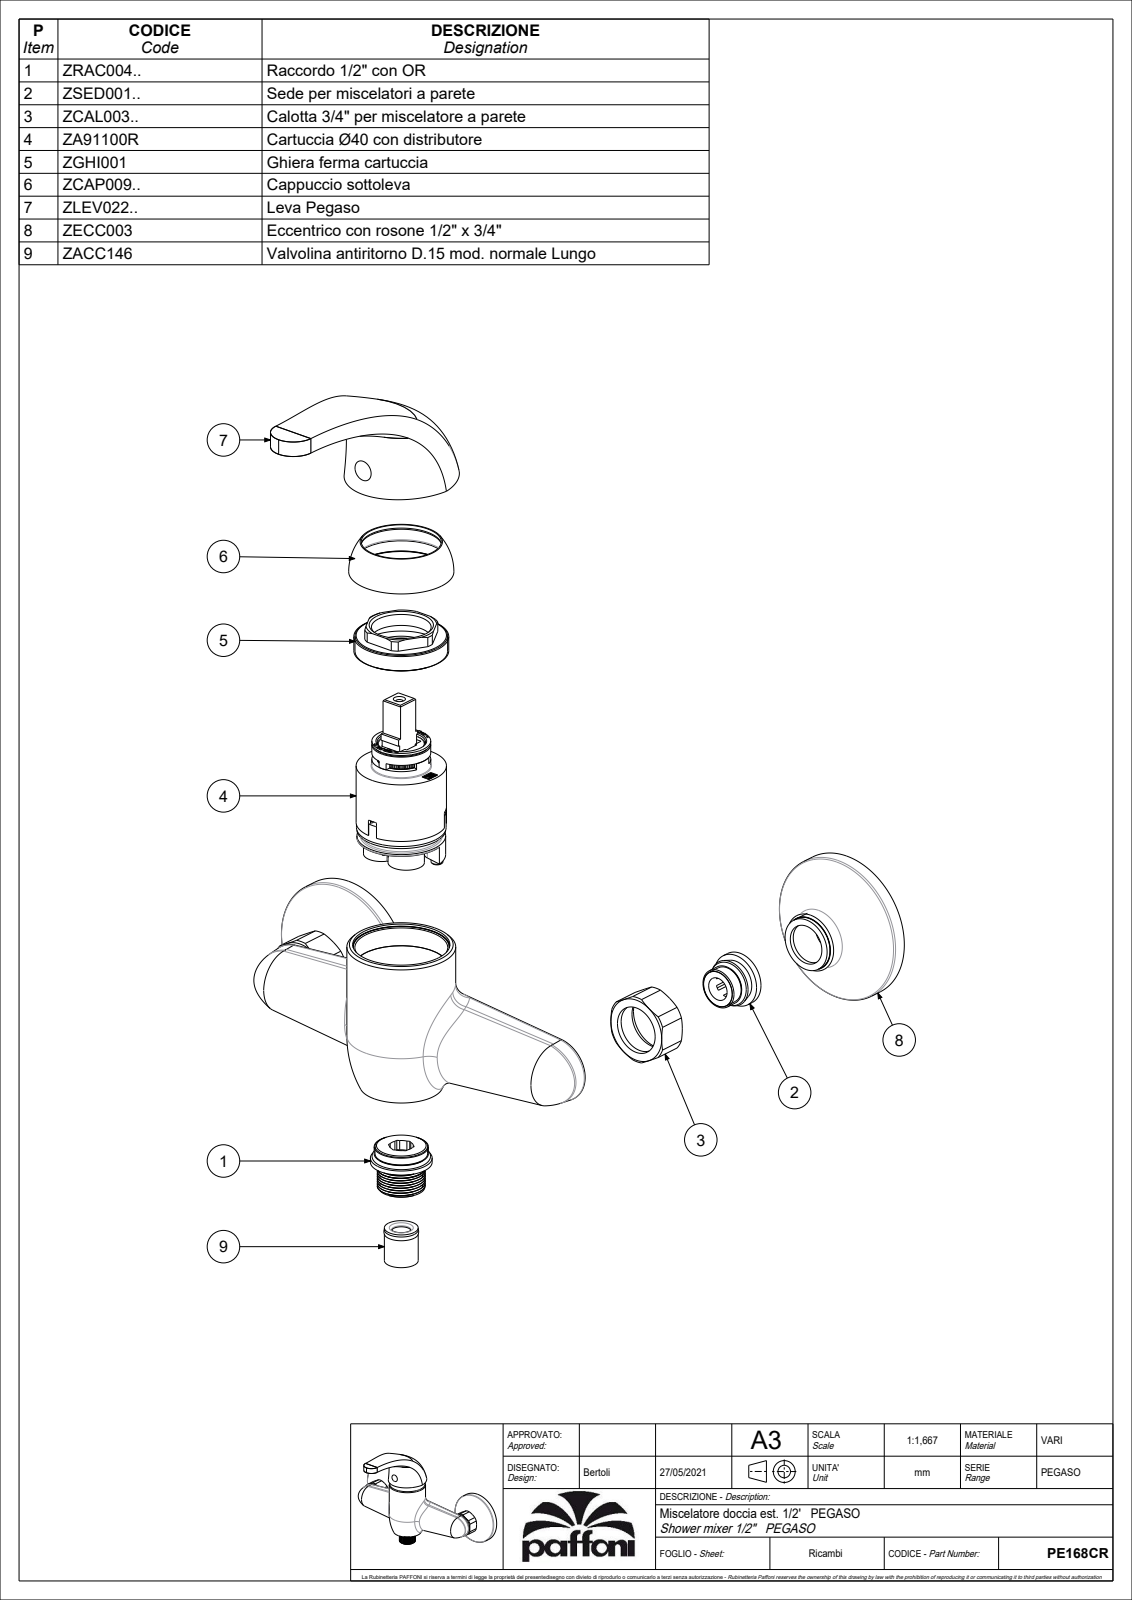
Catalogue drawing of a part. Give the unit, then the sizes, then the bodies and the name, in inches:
Units: inches
Overall size (bounding box): 8.504 × 6.198 × 5.377
Round holes (diameter × count): ⌀1.051 ×2, ⌀0.236 ×1
Round bosses / shafts (diameter × count): ⌀0.827 ×3, ⌀2.598 ×2, ⌀1.039 ×2, ⌀1.874 ×1, ⌀1.063 ×1, ⌀0.315 ×1, ⌀0.197 ×1
Partial cylindrical surfaces — rounded edges, fillets, slot ends (radius × count): R0.039 ×8, R0.61 ×2, R0.154 ×1
Main face-to-face distances: 1.142, 1.358, 1.299, 0.059, 0.914, 2.953, 0.807, 2.106, 2.165, 3.248
Hole centre spacings: 3.831, 5.906
Volume: 23.52 in³ · Surface area: 102.9 in²
Bodies: 1 solid, 262 faces (54 planar, 75 cylindrical, 133 other)
Part name (STEP PRODUCT): PE168CR_SW0001
STEP written by: CREO PARAMETRIC BY PTC INC, 2022124 (CONFIG_CONTROL_DESIGN)
